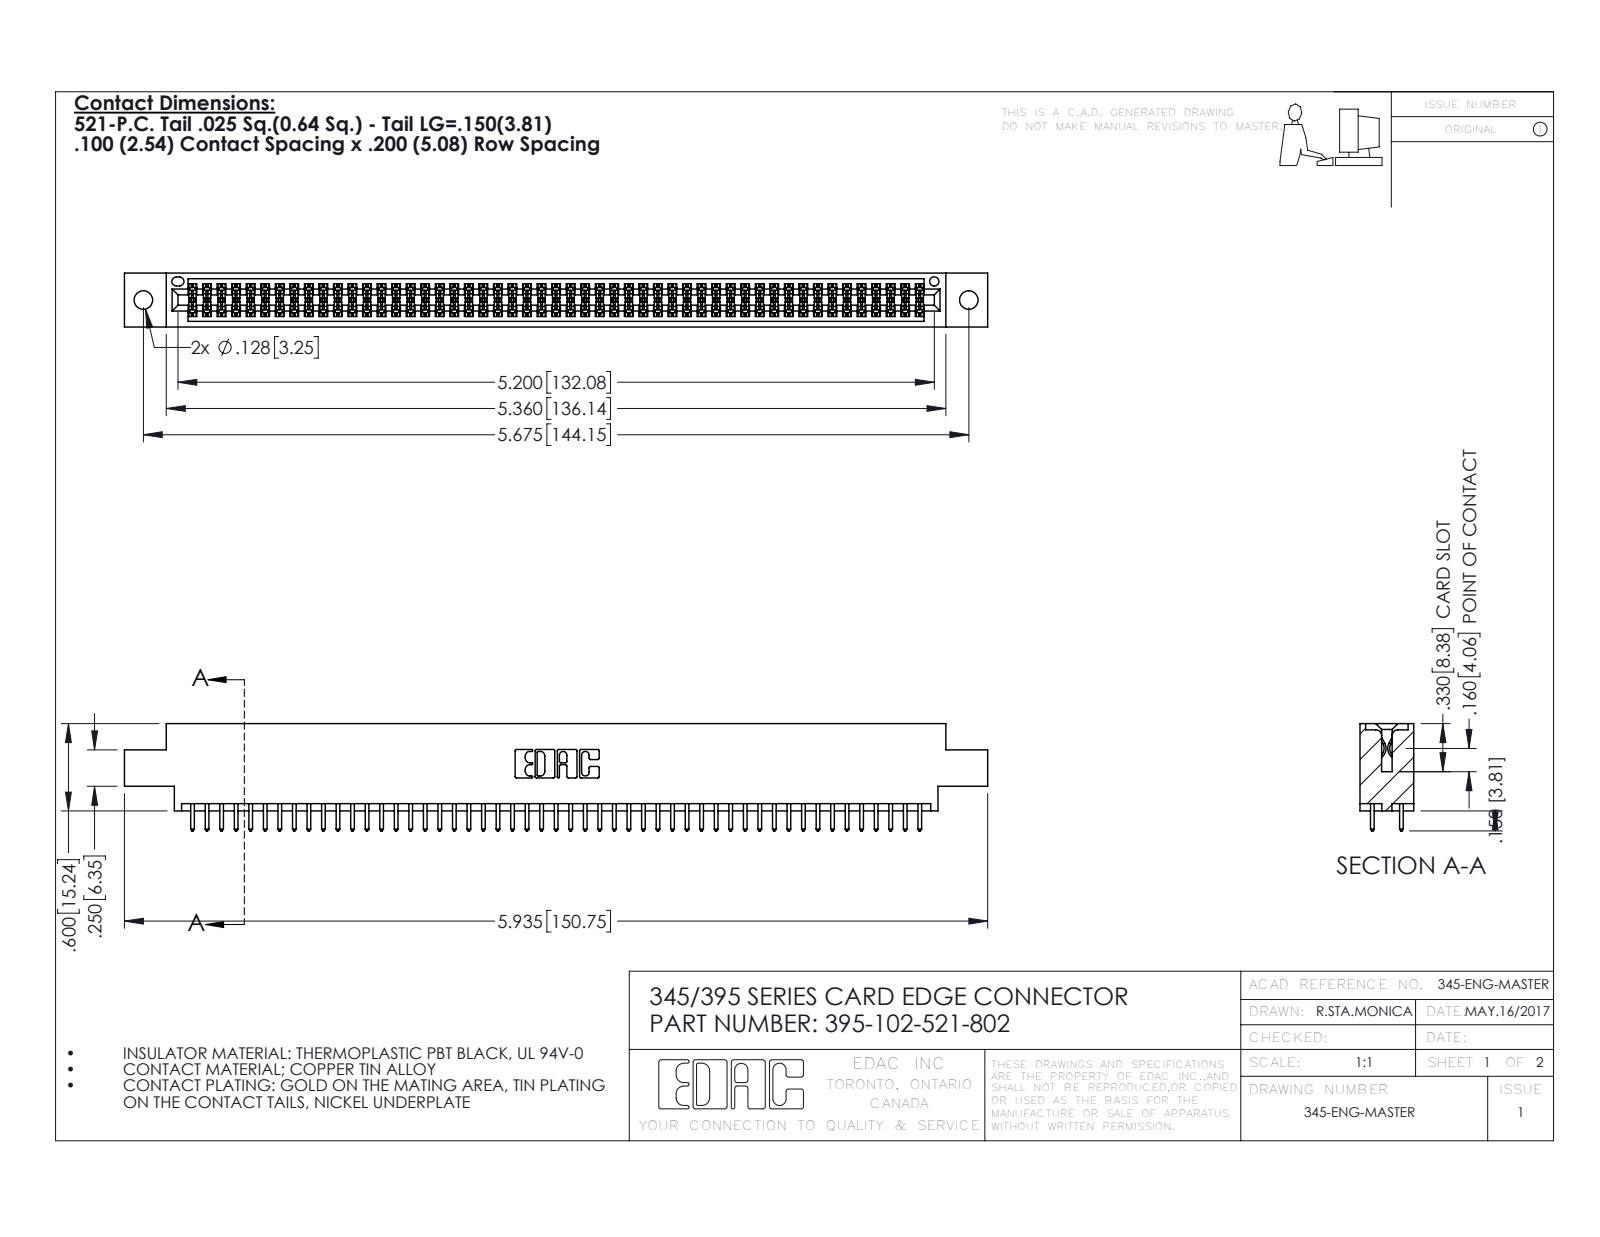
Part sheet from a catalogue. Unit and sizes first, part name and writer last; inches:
Units: inches
Overall size (bounding box): 5.935 × 0.737 × 0.37
Round holes (diameter × count): ⌀0.128 ×2, ⌀0.064 ×1
Partial cylindrical surfaces — rounded edges, fillets, slot ends (radius × count): R0.006 ×153, R0.01 ×102, R0.01 ×22, R0.007 ×6, R0.031 ×6, R0.026 ×3, R0.014 ×2, R0.019 ×2
Main face-to-face distances: 0.298, 0.072, 0.2, 0.37, 0.098, 0.272, 0.025, 0.225, 0.175, 0.149
Hole centre spacings: 0.27, 5.439, 5.675
Volume: 0.887 in³ · Surface area: 32.95 in²
Bodies: 103 solids, 5230 faces (3450 planar, 1780 cylindrical, 0 other)
Part name (STEP PRODUCT): 395-102-521-802; 345 Part_0.170 Offset - 0.128 Dia; 345-292-001_345-293-121
STEP written by: SolidWorks 2016 (CONFIG_CONTROL_DESIGN)
